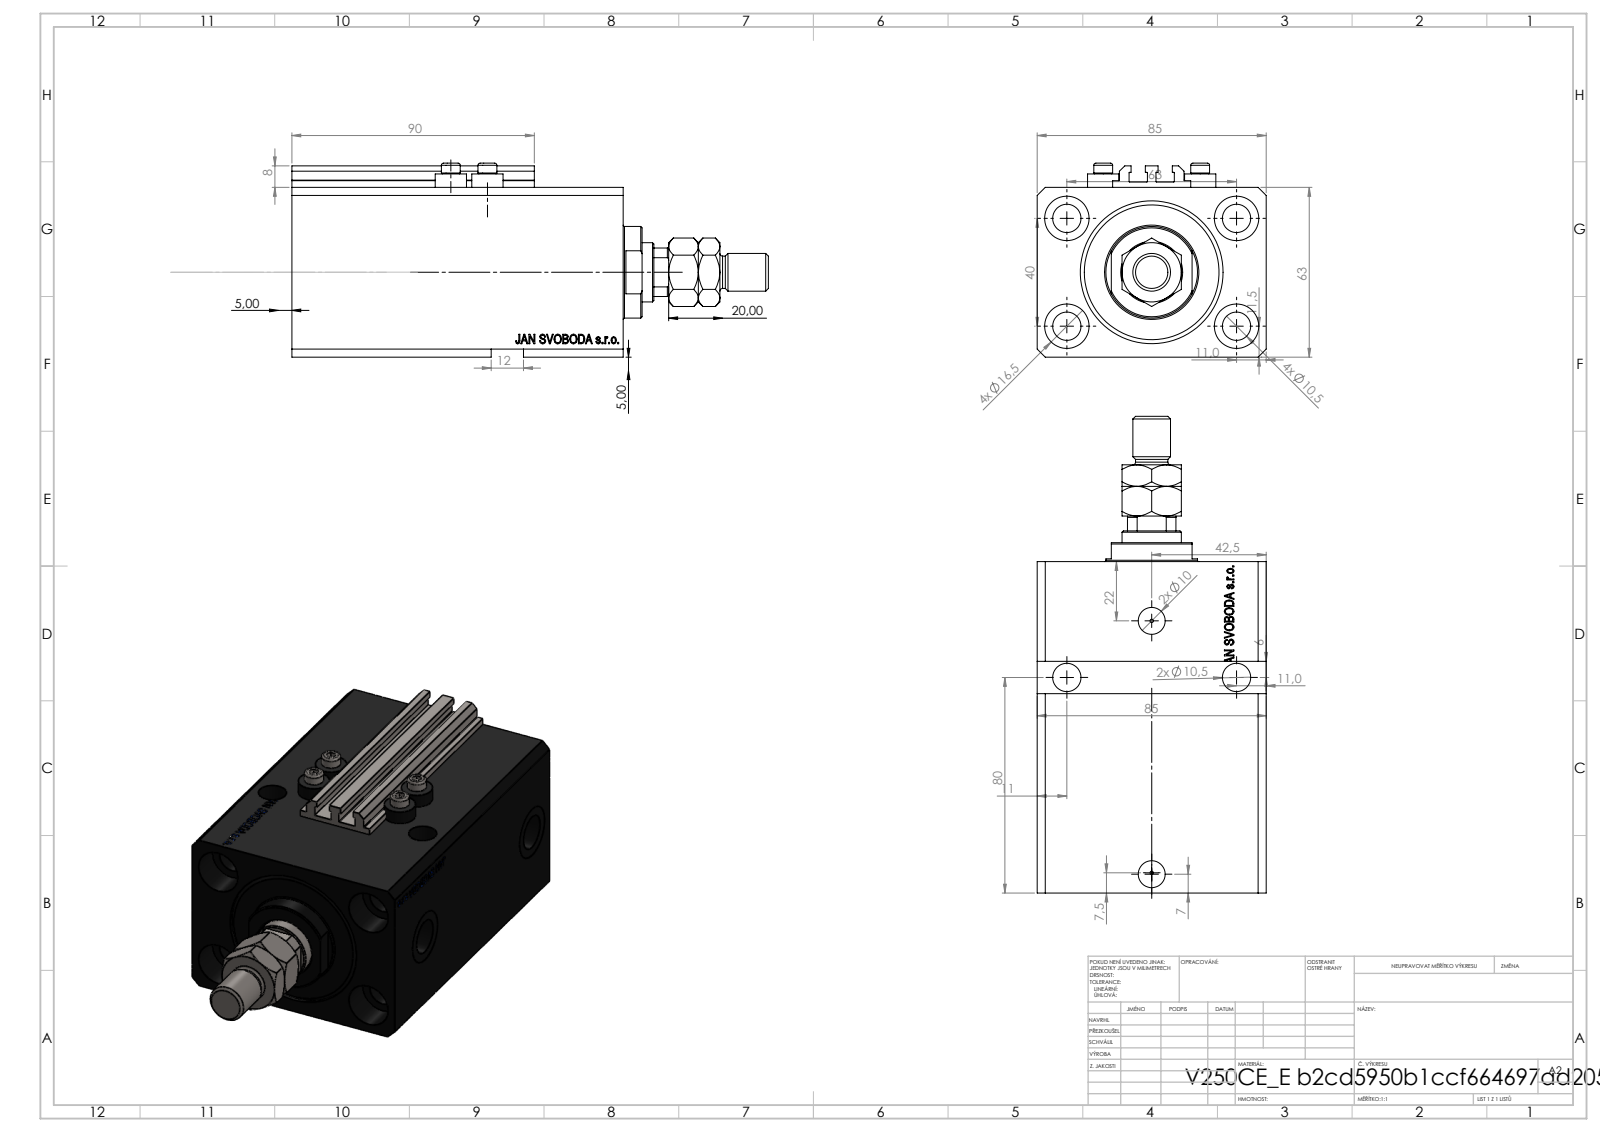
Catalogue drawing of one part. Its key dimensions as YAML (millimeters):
part_name: "V250CE_VC_E; V250CE_E_Body; MTA; ALLEN BOLT V250CE (+1 more)"
step_written_by: "SolidWorks 2019 (CONFIG_CONTROL_DESIGN)"
units: millimeters
bodies: {solids: 9, faces: 1156, planar: 550, cylindrical: 150, other: 456}
overall_size: [177, 85, 72]
volume: 567178
surface_area: 122369
round_holes:
  - {diameter: 10.5, count: 8}
  - {diameter: 1.25, count: 4}
  - {diameter: 4, count: 4}
  - {diameter: 16.5, count: 4}
  - {diameter: 10, count: 2}
  - {diameter: 13.16, count: 2}
  - {diameter: 20, count: 2}
  - {diameter: 12.5, count: 1}
  - {diameter: 22, count: 1}
  - {diameter: 40, count: 1}
  - {diameter: 53, count: 1}
round_bosses_or_shafts:
  - {diameter: 11.6, count: 4}
  - {diameter: 7, count: 4}
  - {diameter: 34, count: 1}
  - {diameter: 14, count: 1}
  - {diameter: 12, count: 1}
partial_cylinders:
  - {radius: 0.2, count: 10}
  - {radius: 10.5, count: 1}
face_to_face_distances: [63, 85, 17, 123, 106, 11.4, 94.6, 111.6, 3, 65]
hole_center_spacings: [37.31, 63, 13.6, 15.4, 24.96, 27.54, 33.62, 36]
